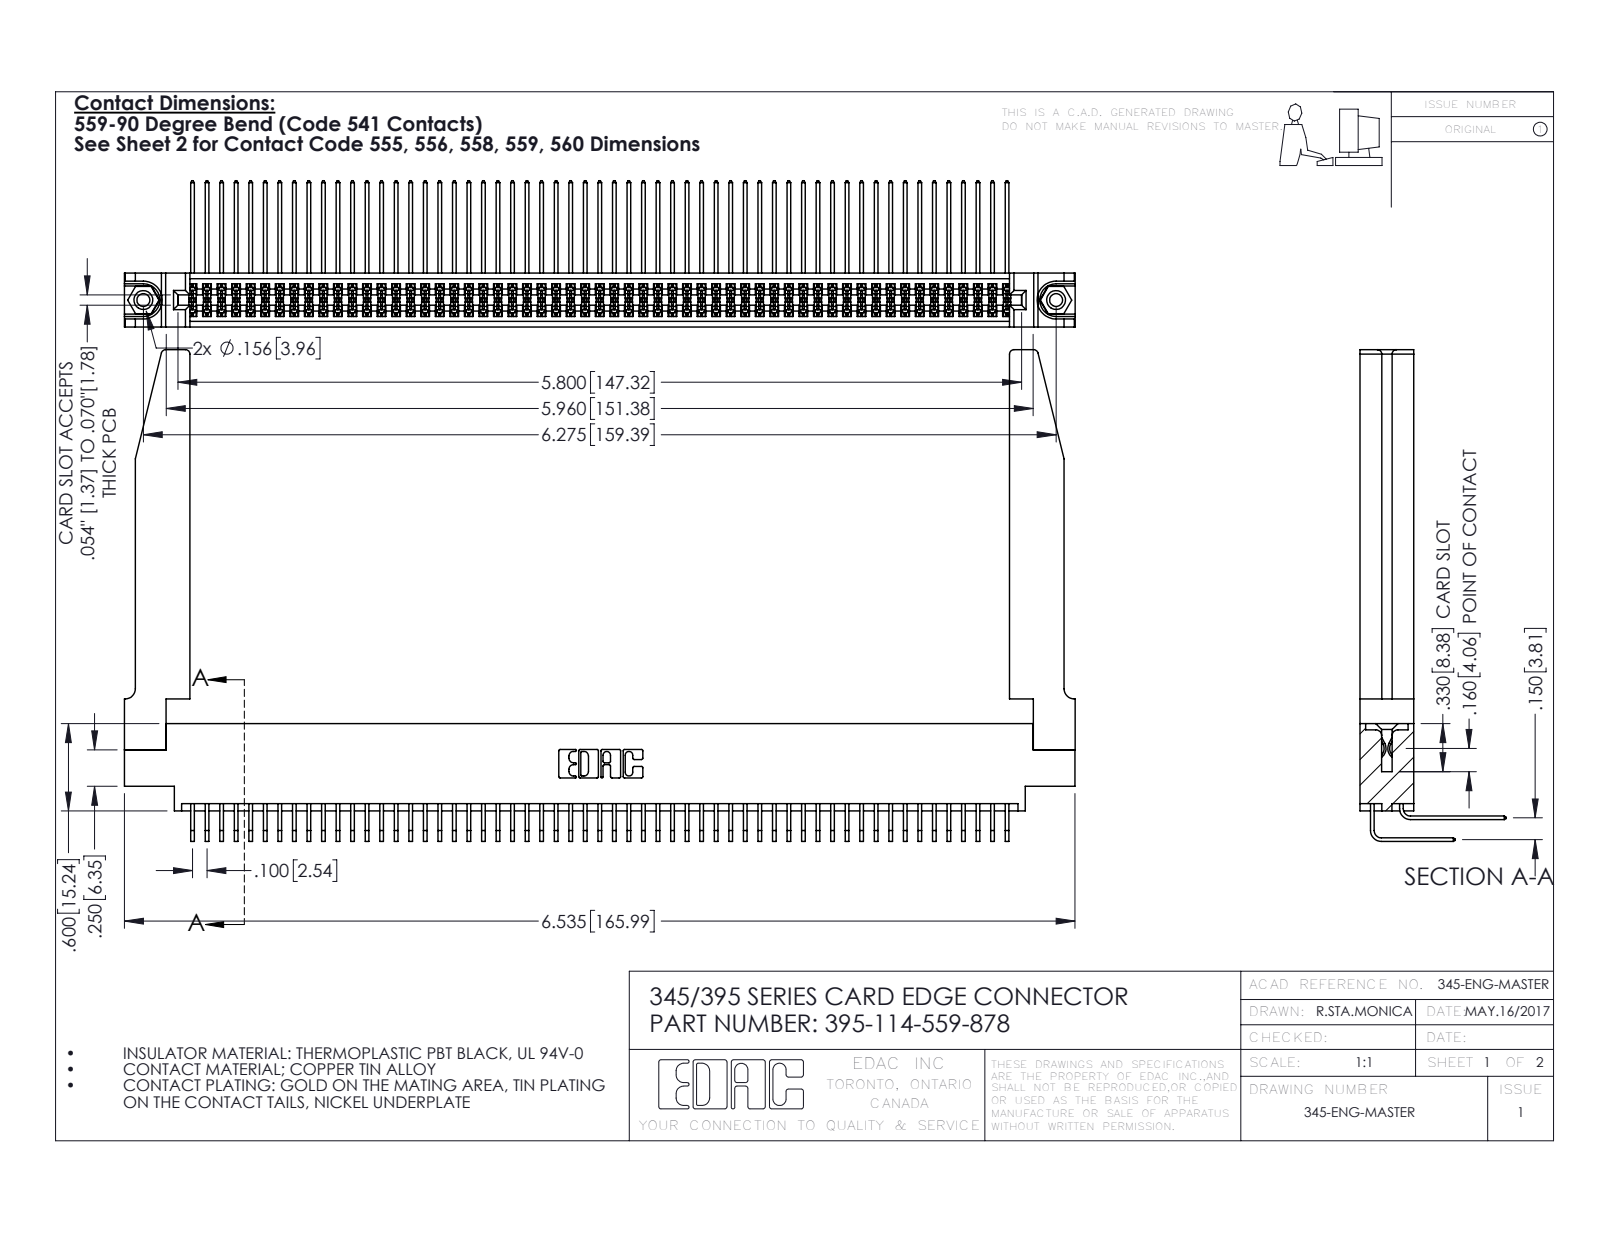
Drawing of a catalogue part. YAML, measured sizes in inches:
part_name: "345-220-078_345-220-078; 395-114-559-878; 345-292-001_558 559 Tail - 1; 345-292-001_559 Tail - 2 (+2 more)"
step_written_by: "SolidWorks 2016 (CONFIG_CONTROL_DESIGN)"
units: inches
bodies: {solids: 119, faces: 6292, planar: 4216, cylindrical: 2024, other: 52}
overall_size: [6.536, 3.379, 1.005]
volume: 1.5
surface_area: 54.58
round_holes:
  - {diameter: 0.089, count: 2}
  - {diameter: 0.125, count: 2}
  - {diameter: 0.156, count: 2}
  - {diameter: 0.064, count: 1}
round_bosses_or_shafts:
  - {diameter: 0.155, count: 2}
partial_cylinders:
  - {radius: 0.006, count: 171}
  - {radius: 0.01, count: 22}
  - {radius: 0.03, count: 8}
  - {radius: 0.007, count: 6}
  - {radius: 0.031, count: 6}
  - {radius: 0.026, count: 3}
  - {radius: 0.014, count: 2}
  - {radius: 0.019, count: 2}
face_to_face_distances: [0.072, 0.37, 0.298, 0.098, 0.272, 0.025, 0.2, 0.225, 0.15, 0.175]
hole_center_spacings: [0.27, 6.039, 6.275]
